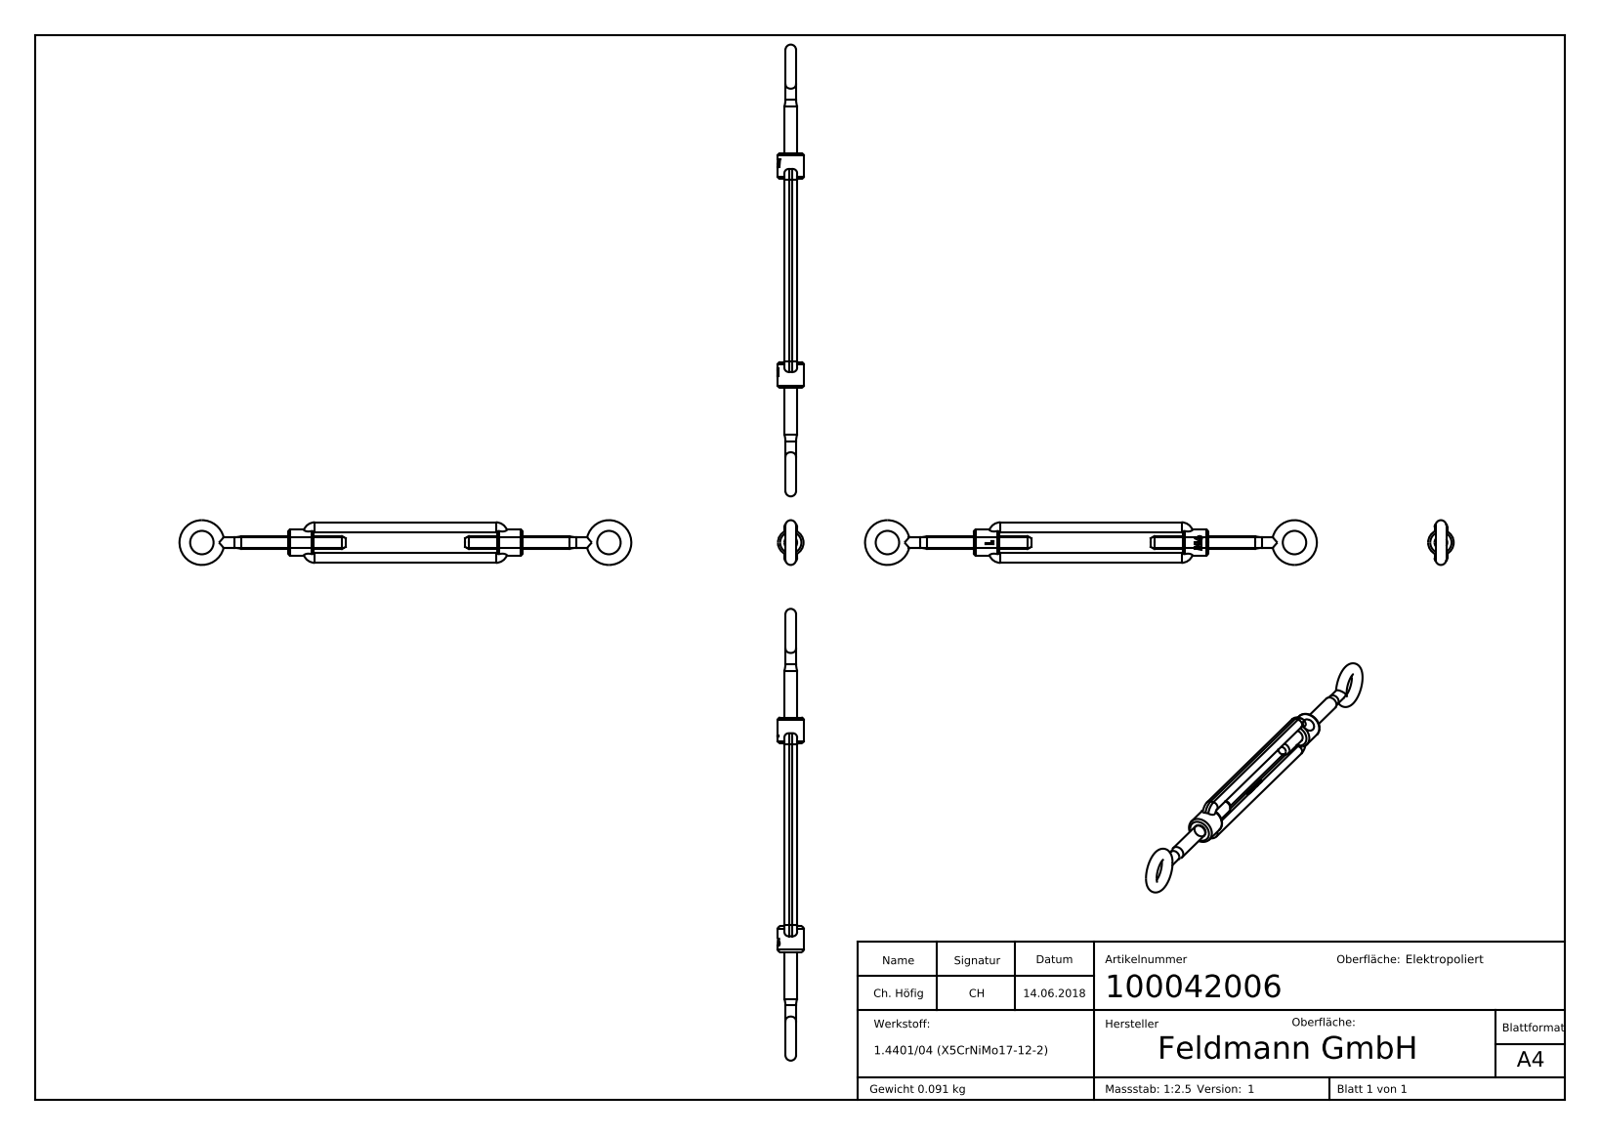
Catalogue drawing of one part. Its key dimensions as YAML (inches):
part_name: "10004200X Teil2_100042006 Teil2; 10004200X Teil3_100042006 Teil3; 10004200X Teil1_100042006 Teil1; 100042006"
step_written_by: "SolidWorks 2015 (CONFIG_CONTROL_DESIGN)"
units: inches
bodies: {solids: 3, faces: 378, planar: 162, cylindrical: 32, other: 184}
overall_size: [8.346, 0.827, 0.472]
volume: 0.696
surface_area: 12.9
round_holes:
  - {diameter: 0.197, count: 1}
round_bosses_or_shafts:
  - {diameter: 0.472, count: 1}
  - {diameter: 0.236, count: 1}
partial_cylinders:
  - {radius: 0.039, count: 4}
  - {radius: 0.089, count: 4}
  - {radius: 0.217, count: 4}
  - {radius: 0.235, count: 1}
face_to_face_distances: [0.177, 0.571, 0.748, 0.394, 0.472, 3.858, 4.331, 3.386, 1.063, 3.268]
